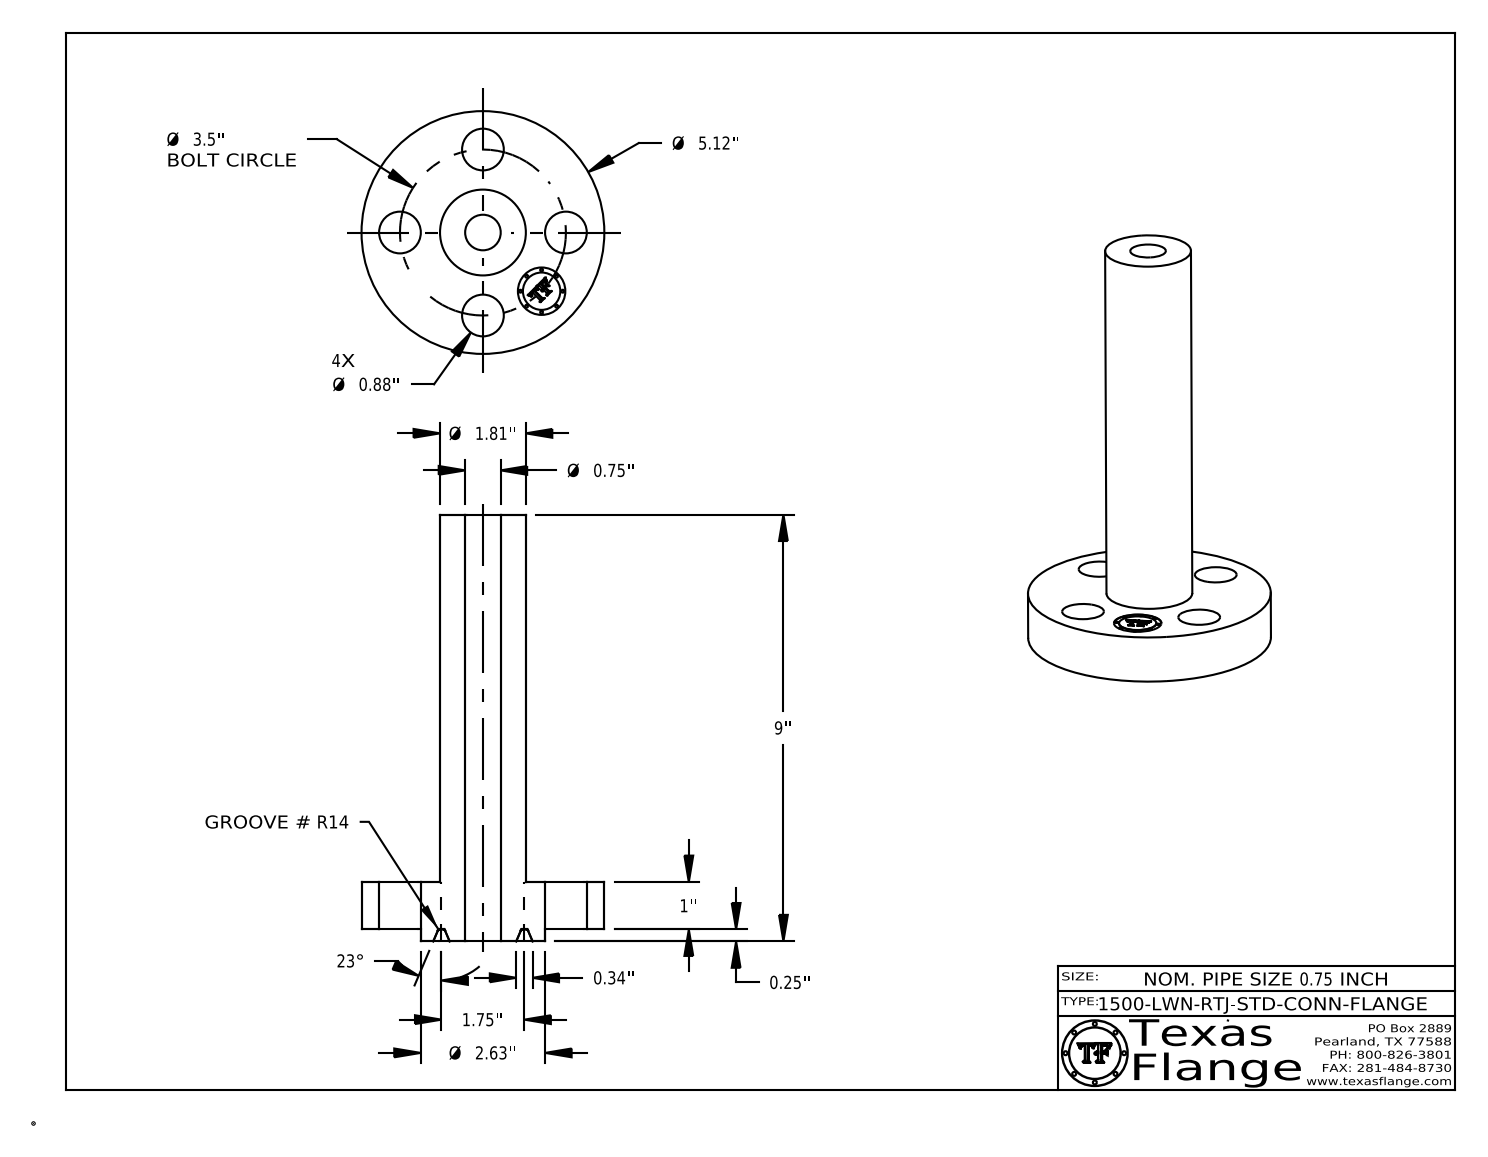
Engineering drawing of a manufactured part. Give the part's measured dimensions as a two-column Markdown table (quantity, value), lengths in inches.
| quantity | value |
| --- | --- |
| part name | 0.75-1500-LWN-RTJ-STD-CONN-FLANGE |
| STEP written by | CATIA V5 STEP AP214 (AUTOMOTIVE_DESIGN) |
| units | inches |
| bodies | 1 solid, 419 faces (371 planar, 40 cylindrical, 8 other) |
| overall size | 9 × 5.12 × 5.12 |
| volume | 35.15 in³ |
| surface area | 131.7 in² |
| round holes (diameter × count) | 0.88 × 4, 0.75 × 1, 1 × 1 |
| round bosses / shafts (diameter × count) | 0.061 × 8, 5.12 × 1, 2.625 × 1, 1.81 × 1, 0.788 × 1 |
| main face-to-face distances | 1, 0.25, 1.25, 9, 8.75, 7.75, 1.245, 0.995, 7.755, 0.298 |
| hole center spacings | 1.75, 2.475, 1.339, 3.233, 3.5 |
